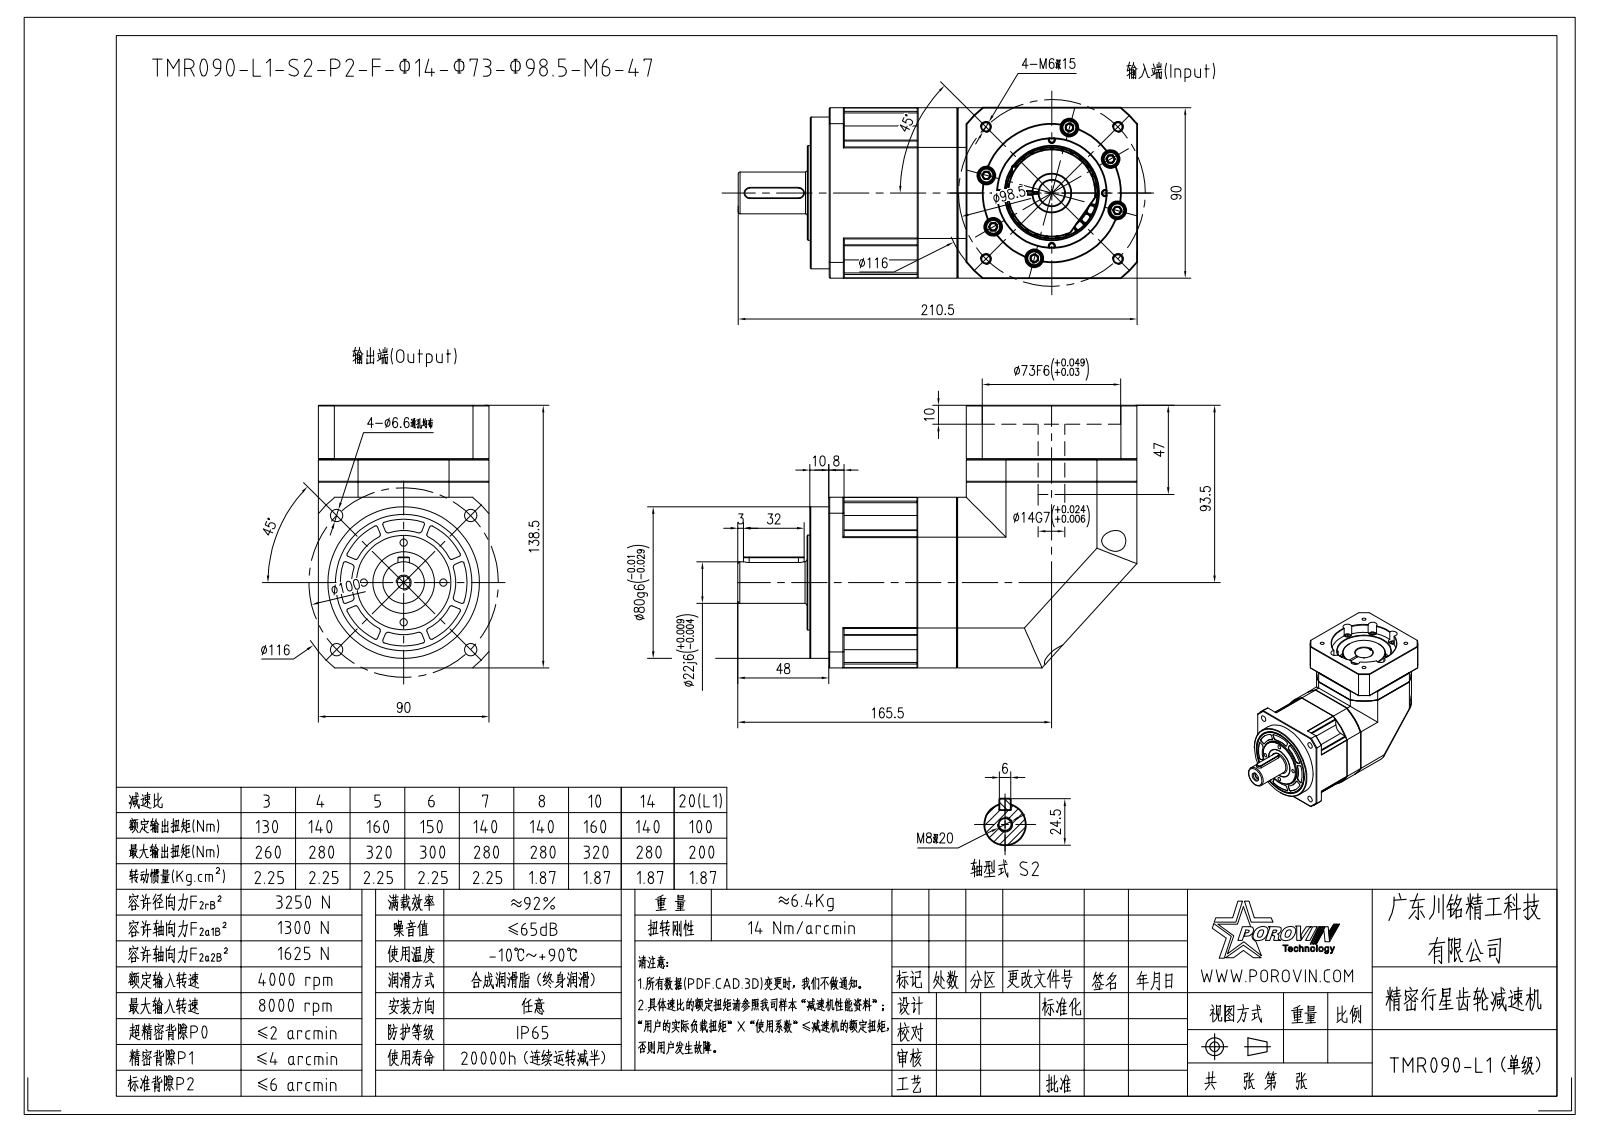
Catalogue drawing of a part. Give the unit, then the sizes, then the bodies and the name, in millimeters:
Units: millimetres
Overall size (bounding box): 210.5 × 138.5 × 90
Round holes (diameter × count): ⌀5.4 ×12, ⌀5.5 ×12, ⌀9.5 ×12, ⌀4.2 ×7, ⌀5 ×5, ⌀6.5 ×5, ⌀4 ×4, ⌀6.6 ×4, ⌀6.68 ×4, ⌀11 ×4, ⌀6.8 ×1, ⌀8.4 ×1
Round bosses / shafts (diameter × count): ⌀8.5 ×12, ⌀8 ×12, ⌀5 ×12, ⌀10 ×4, ⌀9.88 ×4, ⌀6 ×4, ⌀80 ×1, ⌀78 ×1
Partial cylindrical surfaces — rounded edges, fillets, slot ends (radius × count): R1 ×92, R7.5 ×4, R51 ×3, R3 ×2, R58 ×2, R4 ×1, R5.25 ×1, R36.5 ×1
Main face-to-face distances: 90, 12, 21.3, 21.5, 10, 26, 110, 2.5, 28.5, 31.3
Hole centre spacings: 35.75, 27.36, 38.16, 66.06, 66.53, 67.94, 17.39, 52.85
Volume: 1 344 000 mm³ · Surface area: 212 444 mm²
Bodies: 43 solids, 1295 faces (516 planar, 548 cylindrical, 231 other)
Part name (STEP PRODUCT): HEXAGON_SOCKET_HEAD_CAP_S-30720; HEXAGON_SOCKET_HEAD_CAP_SC-9242; HEXAGON_SOCKET_HEAD_CAP_S-20065; SPRING_LOCK_WASHERS--NORM-30785 (+8 more)
STEP written by: CREO PARAMETRIC BY PTC INC, 2020053 (CONFIG_CONTROL_DESIGN)
